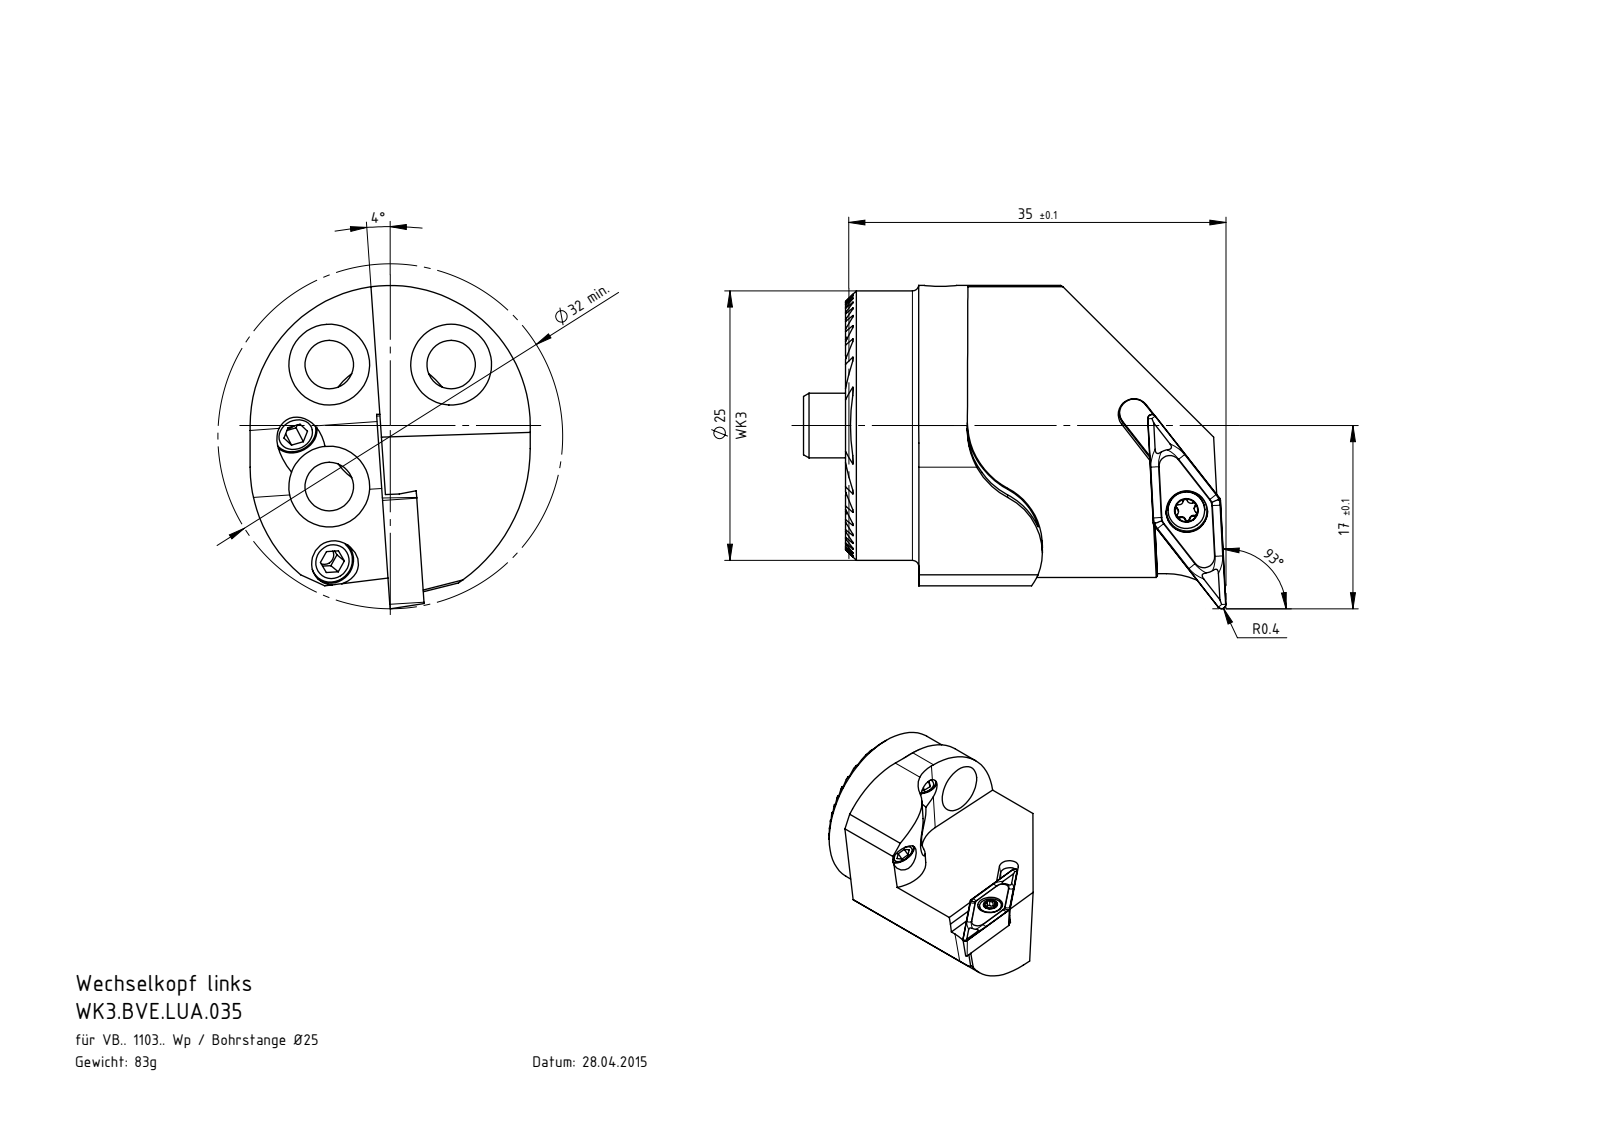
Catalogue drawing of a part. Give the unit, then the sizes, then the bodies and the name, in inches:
Units: inches
Overall size (bounding box): 1.535 × 1.169 × 1.024
Round holes (diameter × count): ⌀0.094 ×3, ⌀0.098 ×3, ⌀0.165 ×3, ⌀0.177 ×3, ⌀0.295 ×3, ⌀0.067 ×2, ⌀0.118 ×2, ⌀0.13 ×2, ⌀0.081 ×1, ⌀0.11 ×1, ⌀0.152 ×1, ⌀0.236 ×1
Round bosses / shafts (diameter × count): ⌀0.118 ×3, ⌀0.157 ×2, ⌀0.984 ×1, ⌀0.472 ×1, ⌀0.134 ×1, ⌀0.098 ×1
Partial cylindrical surfaces — rounded edges, fillets, slot ends (radius × count): R0.005 ×20, R0.008 ×6, R0.014 ×5, R0.512 ×3, R0.276 ×2, R0.014 ×1, R0.053 ×1, R0.236 ×1
Main face-to-face distances: 0.17, 0.043, 0.128, 0.213, 0.341, 0.085, 0.298, 0.085, 0.113, 0.383
Hole centre spacings: 0.315, 0.446, 0.63
Volume: 0.649 in³ · Surface area: 10.38 in²
Bodies: 12 solids, 387 faces (184 planar, 98 cylindrical, 105 other)
Part name (STEP PRODUCT): VBMT110304; KVT_MB_600_030; WK3.BVE.LUA.035; WCA-ER2.001.006_A (+3 more)
STEP written by: SolidWorks 2017 (AUTOMOTIVE_DESIGN)
